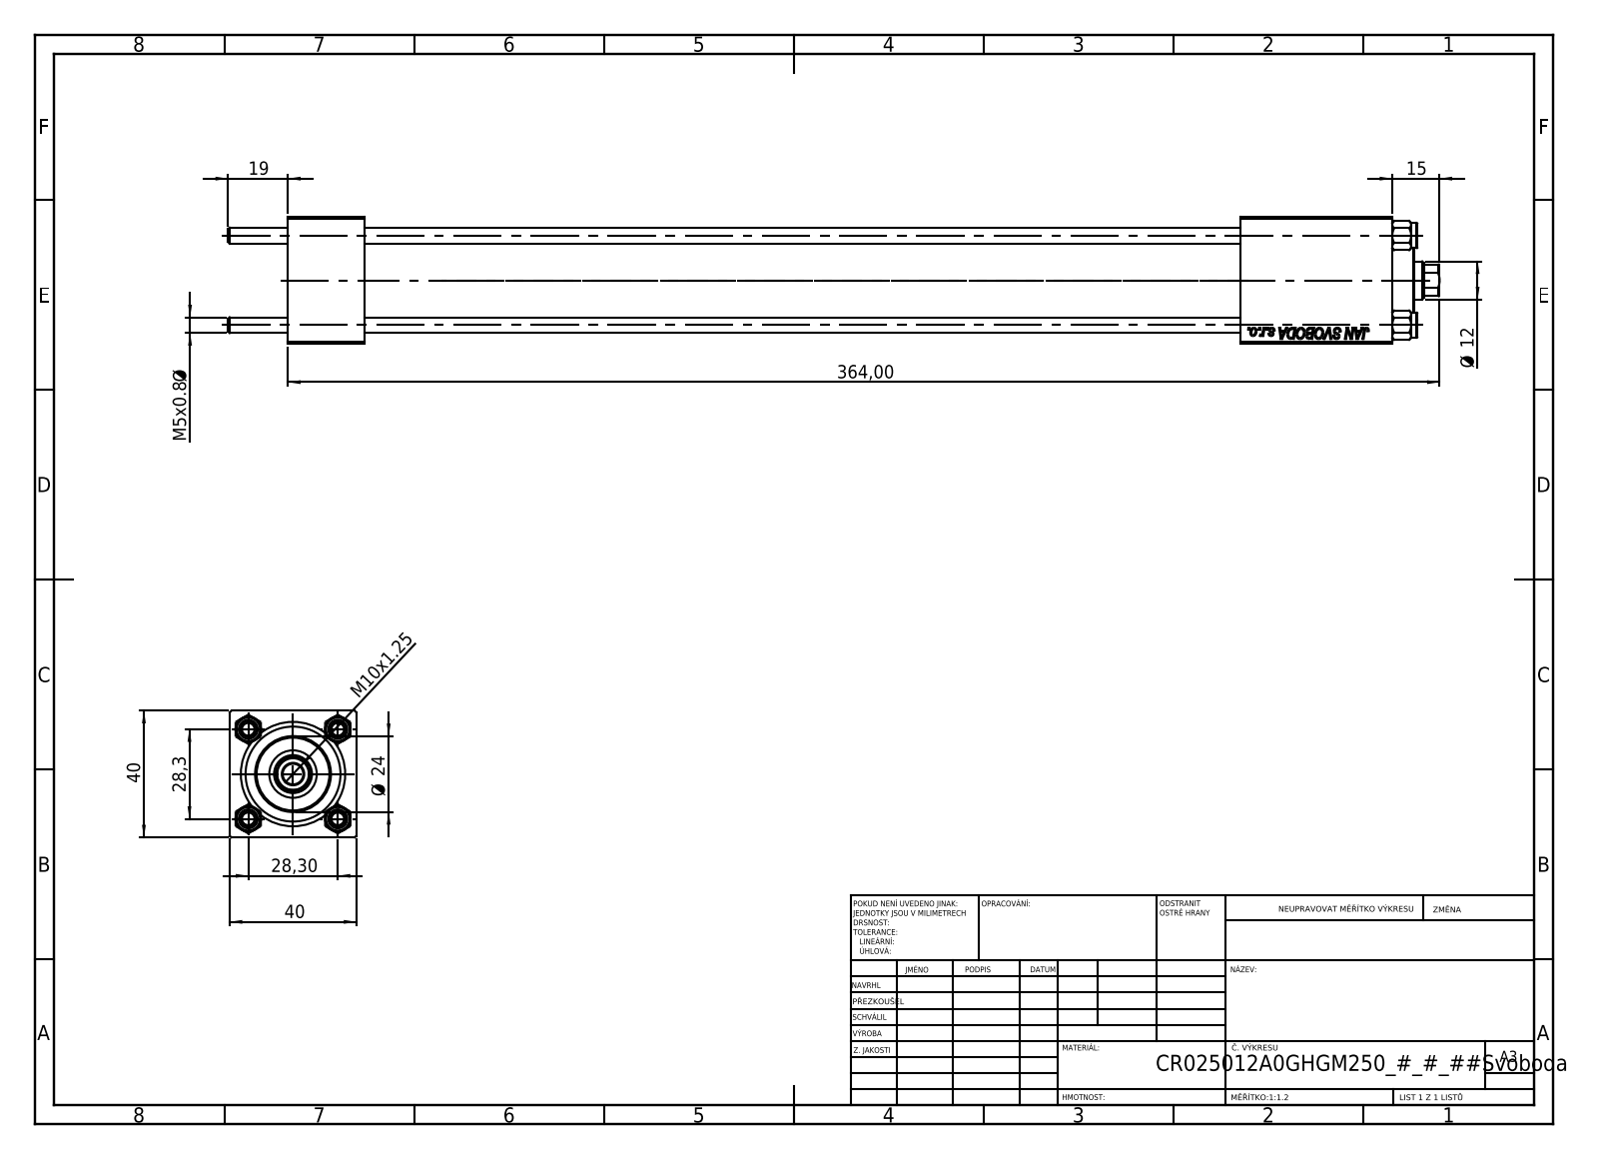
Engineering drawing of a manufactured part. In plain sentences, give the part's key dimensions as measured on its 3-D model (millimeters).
The part is named "V215_VC_A; V215CR_VCP; NUT_M5; CR025_012_A_0_G_A_G_M_020_+#_##_TYCINKA (+1 more)". Its 3-D file was written by "SolidWorks 2019 (CONFIG_CONTROL_DESIGN)". It is 11 solids with 1131 faces: 517 planar, 78 cylindrical and 536 other. Overall it measures 383 by 40 by 40 millimeters. Its volume is 249 596 cubic millimeters and its surface area 122 457 square millimeters. Round holes: 4 of diameter 5, 3 of diameter 20, 2 of diameter 7, 2 of diameter 13.16, 1 of diameter 6.5, 1 of diameter 12, 1 of diameter 15, 1 of diameter 25, 1 of diameter 30. Round bosses or shafts: 4 of diameter 8, 1 of diameter 31, 1 of diameter 24. Partial cylindrical surfaces (rounded edges, fillets, slot ends): 1 of radius 5.5. The main face-to-face distances are 40, 24, 349, 325, 320.3, 296.3, 28.7, 301, 277, 19.3. The hole center spacings are 20.01, 28.3, 40.02, 302.
